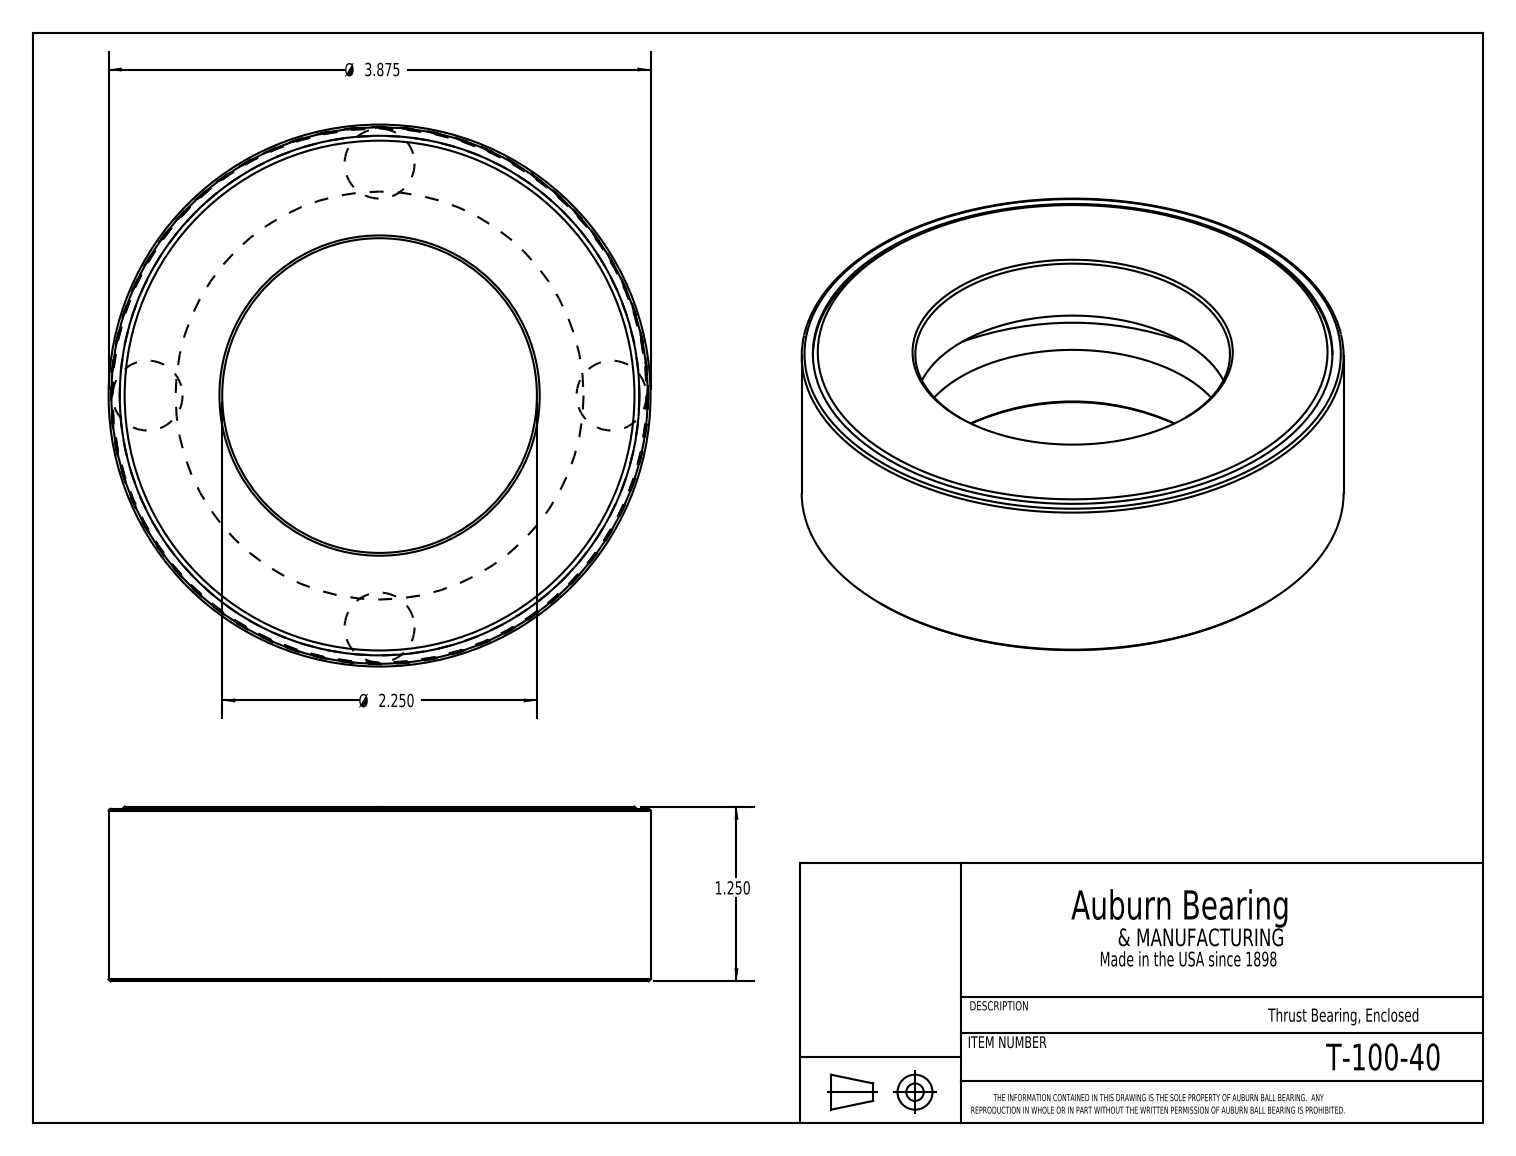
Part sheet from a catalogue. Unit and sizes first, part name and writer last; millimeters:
Units: millimetres
Overall size (bounding box): 98.4 × 98.4 × 31.8
Round holes (diameter × count): ⌀57.2 ×1, ⌀94.4 ×1, ⌀97.4 ×1
Round bosses / shafts (diameter × count): ⌀98.4 ×1, ⌀97.1 ×1
Main face-to-face distances: 12.1, 19.7, 31.8, 7.6, 31.4, 19.3, 11.7, 0.4, 30.9, 18.8
Volume: 116 300 mm³ · Surface area: 46 570 mm²
Bodies: 6 solids, 28 faces (9 planar, 7 cylindrical, 12 other)
Part name (STEP PRODUCT): T-100-40
STEP written by: SolidWorks 2016 (CONFIG_CONTROL_DESIGN)
